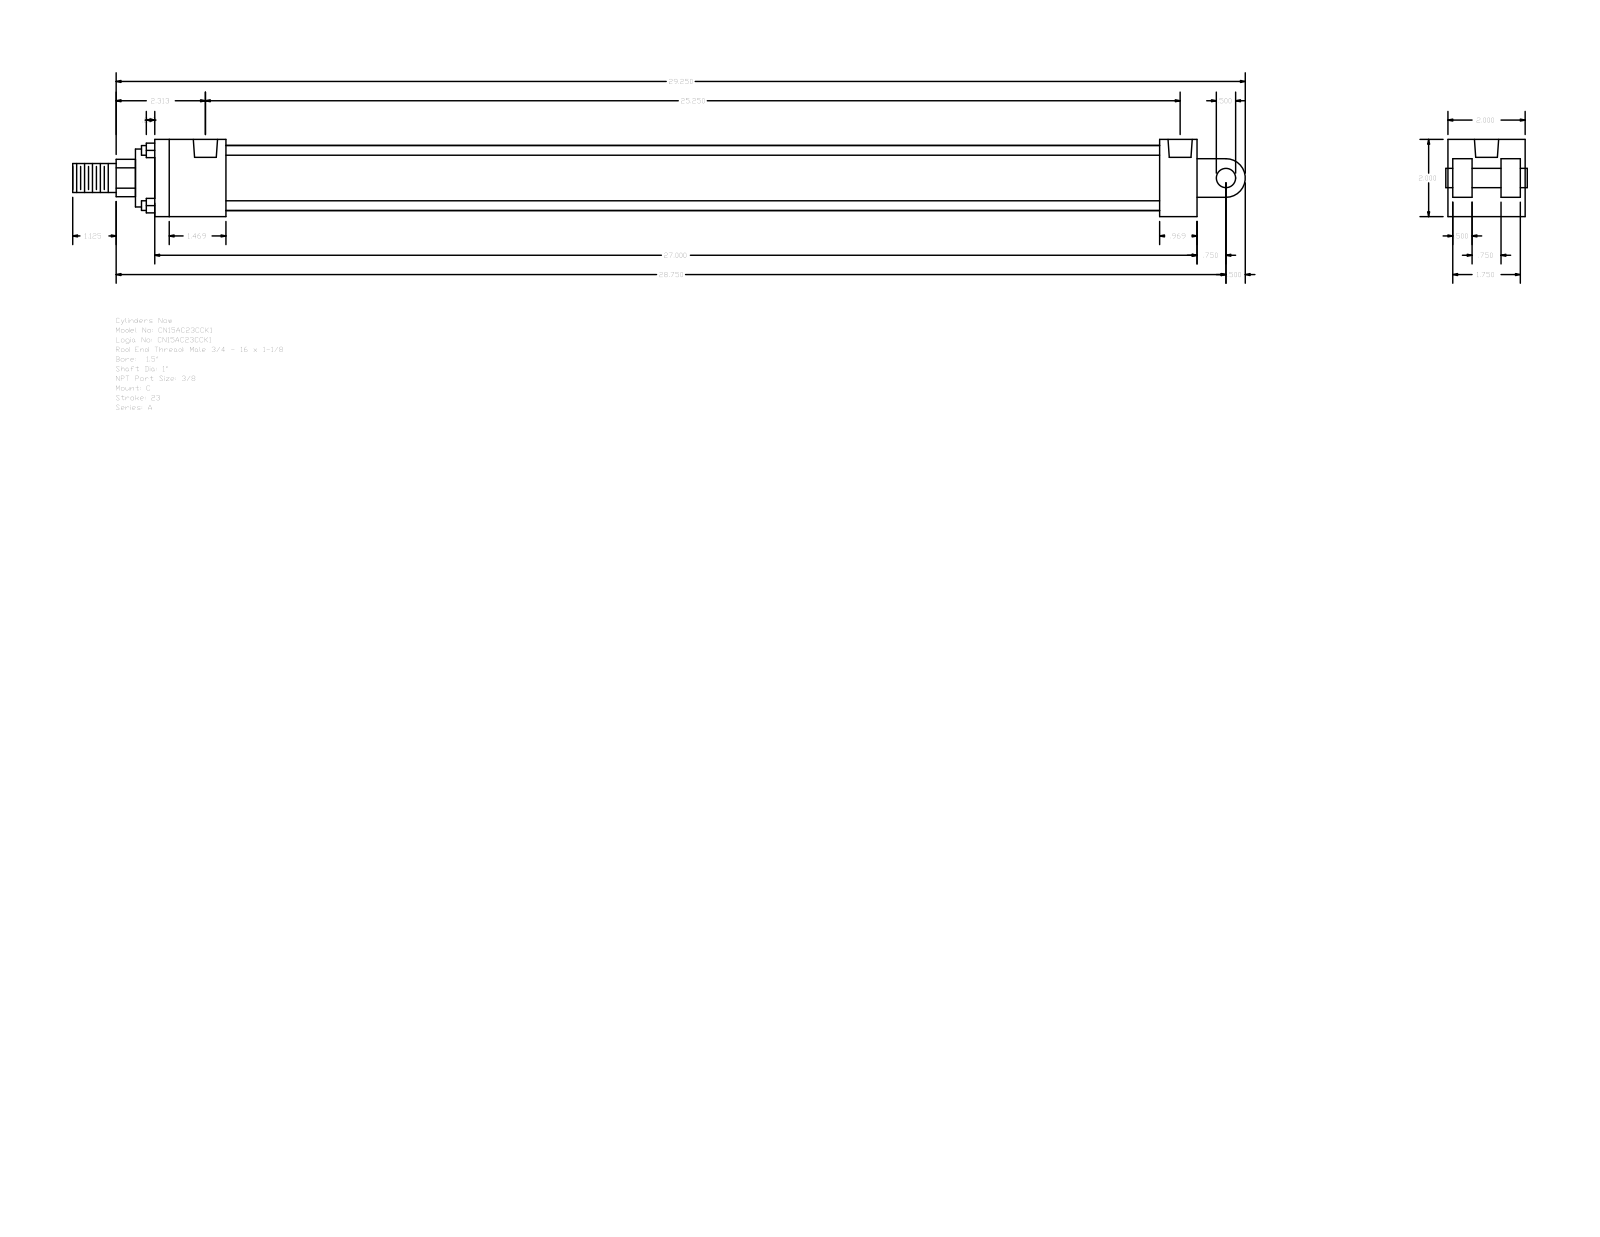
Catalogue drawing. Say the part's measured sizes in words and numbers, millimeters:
The part is named "A_C__0150_1". Its 3-D file was written by "GSSL Pune (CONFIG_CONTROL_DESIGN)". It is 0 solids with 99 faces: 70 planar, 29 cylindrical and 0 other. Overall it measures 771.52 by 50.8 by 50.8 millimeters. Round holes: 4 of diameter 5.56, 2 of diameter 15.93. Round bosses or shafts: 4 of diameter 6.35, 1 of diameter 42.93, 1 of diameter 38.1, 1 of diameter 25.4, 1 of diameter 19.05, 1 of diameter 12.7. Partial cylindrical surfaces (rounded edges, fillets, slot ends): 1 of radius 12.29, 1 of radius 12.7. The main face-to-face distances are 50.8, 12.7, 3.17, 15.87, 47.63, 34.93, 31.76, 685.8, 38.1, 661.19. The hole center spacings are 3.97, 633.41, 637.38, 641.35.
